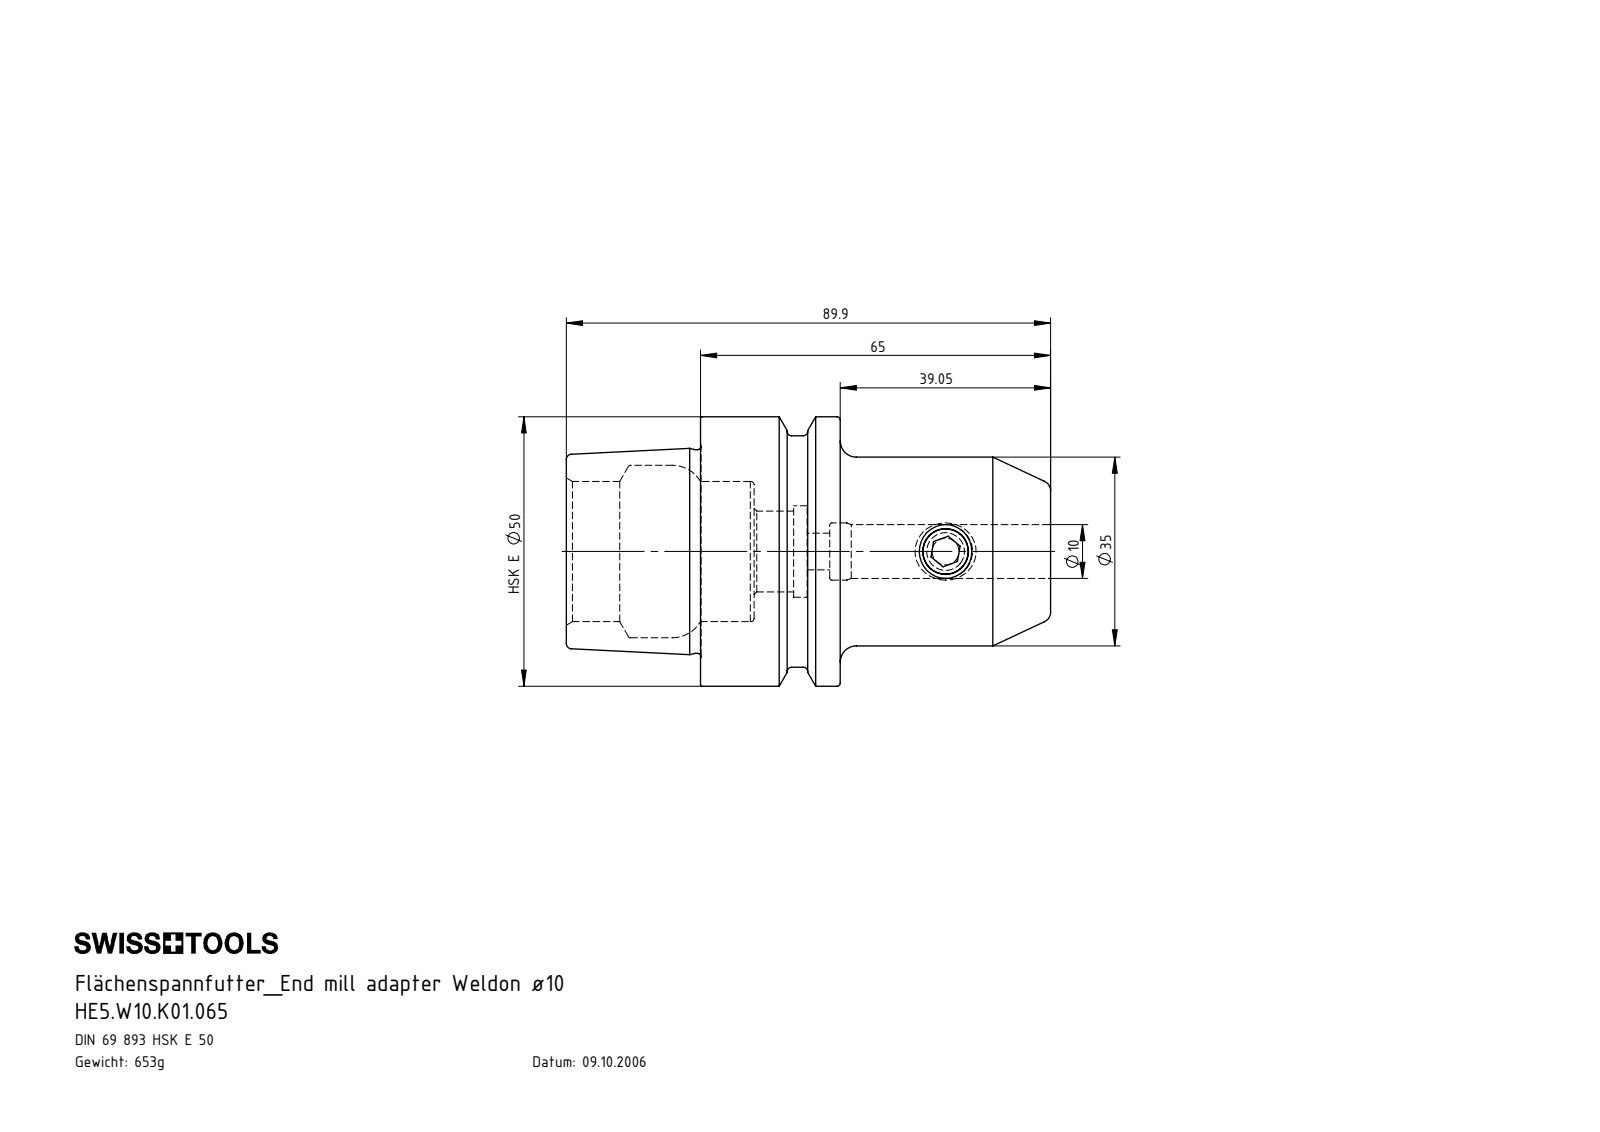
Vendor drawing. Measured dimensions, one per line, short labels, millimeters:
name: HE5.W10.K01.065; W10-ER1.001.012; HE5-W10.K01.065_B_Fertigbearbeitung
written by: SolidWorks 2017 (AUTOMOTIVE_DESIGN)
unit: mm
bodies: 2 solids, 109 faces (19 planar, 30 cylindrical, 60 other)
size: 89.9 × 50 × 50
volume: 83 236 mm³; area: 20 829 mm²
holes: 1× ⌀6.8, 1× ⌀8.5, 1× ⌀10, 1× ⌀10.6, 1× ⌀15, 1× ⌀17, 1× ⌀26, 1× ⌀32
bosses: 1× ⌀50, 1× ⌀42.95, 1× ⌀37.81, 1× ⌀35, 1× ⌀10
face distances: 25.95, 24.9, 50.85, 89.9, 65, 39.05, 34.85, 9.95, 16, 55.05
